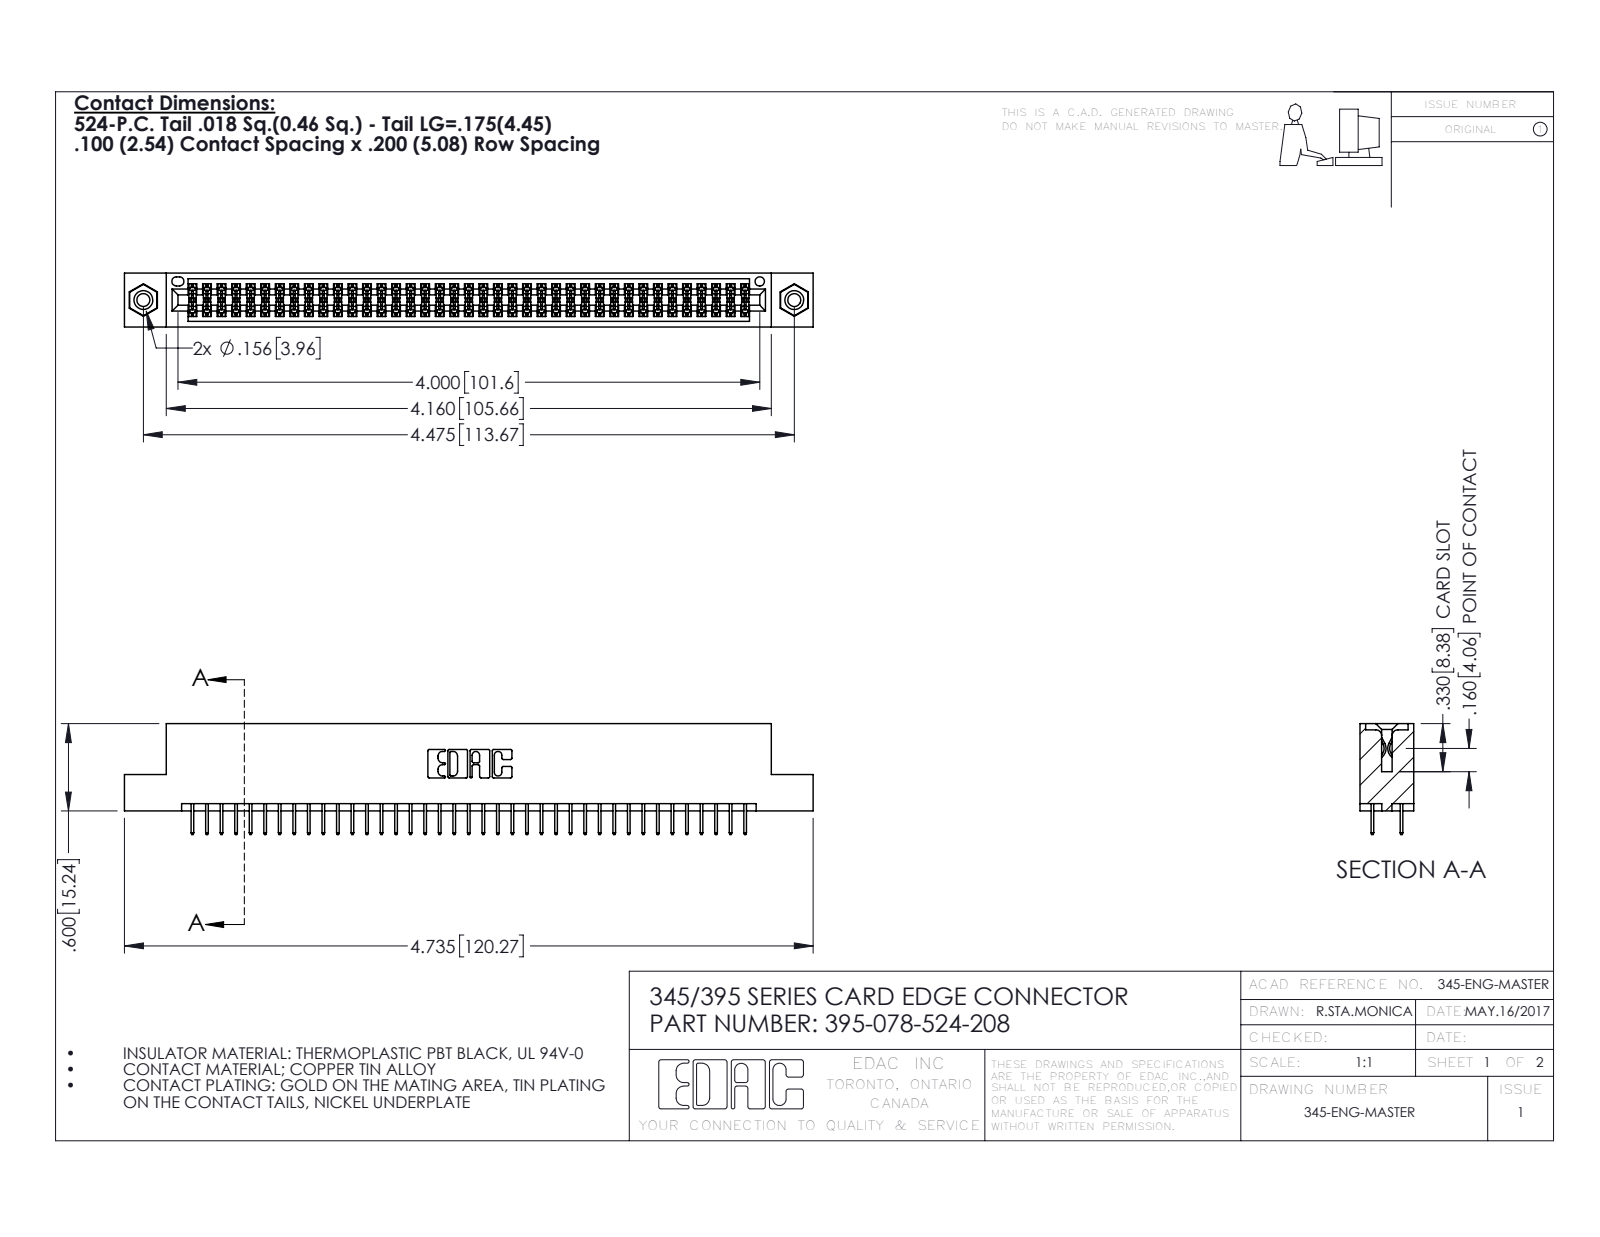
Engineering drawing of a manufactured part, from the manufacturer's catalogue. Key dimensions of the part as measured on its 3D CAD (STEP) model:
Part name (STEP PRODUCT): 345-250-001_345-250-003-102; 345 Part_Flush Mounting Lugs - 0.156 Dia-TI; 395-078-524-208; 345-292-001_345-293-124
STEP written by: SolidWorks 2016 (CONFIG_CONTROL_DESIGN)
Units: inches
Bodies: 81 solids, 4398 faces (3154 planar, 1228 cylindrical, 16 other)
Overall size (bounding box): 4.735 × 0.762 × 0.37
Volume: 0.704 in³ · Surface area: 25.87 in²
Round holes (diameter × count): ⌀0.089 ×2, ⌀0.125 ×2, ⌀0.156 ×2, ⌀0.064 ×1
Round bosses / shafts (diameter × count): ⌀0.155 ×2
Partial cylindrical surfaces — rounded edges, fillets, slot ends (radius × count): R0.006 ×117, R0.01 ×22, R0.007 ×6, R0.031 ×6, R0.026 ×3, R0.014 ×2, R0.019 ×2, R0.022 ×2
Main face-to-face distances: 0.072, 0.298, 0.2, 0.37, 0.098, 0.272, 0.025, 0.225, 0.072, 0.175
Hole centre spacings: 0.27, 4.239, 4.475
